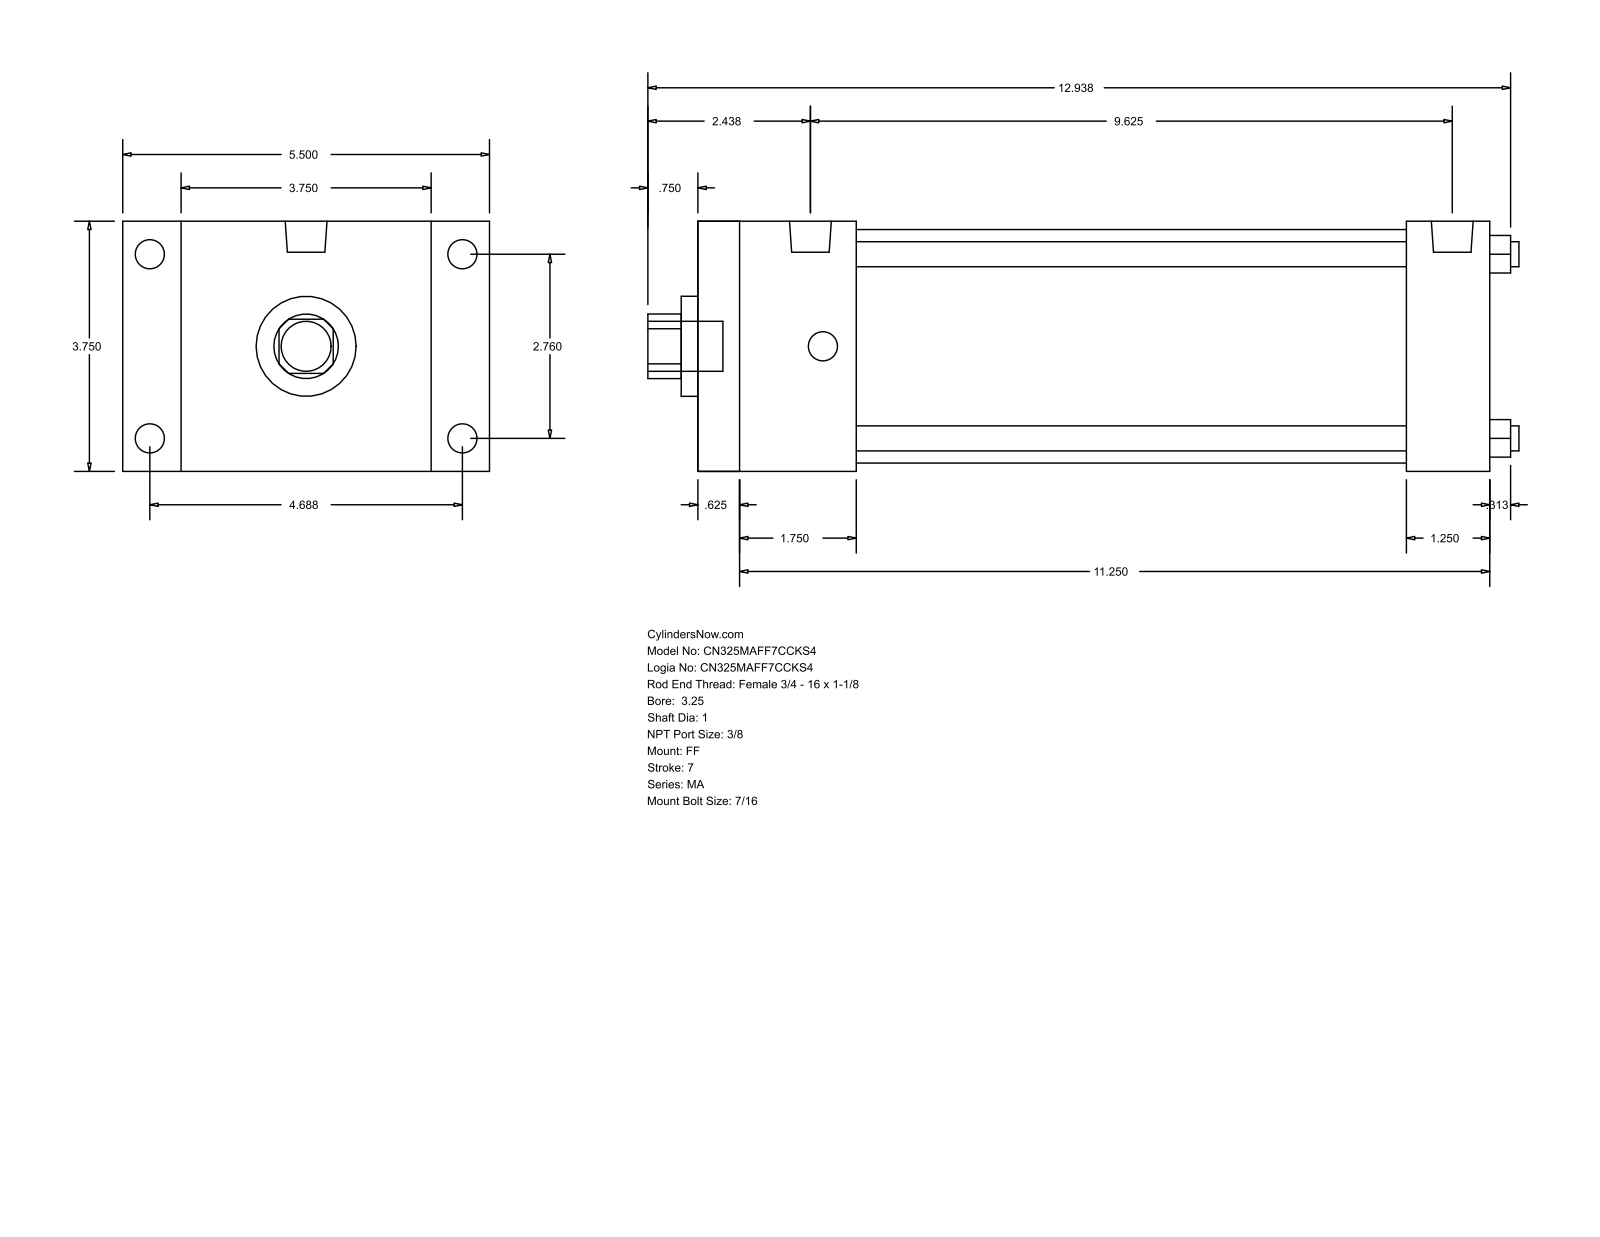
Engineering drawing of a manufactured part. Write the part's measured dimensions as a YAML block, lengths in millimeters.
part_name: "MA_FF__0325_1"
step_written_by: "GSSL Pune (CONFIG_CONTROL_DESIGN)"
units: millimeters
bodies: {solids: 0, faces: 92, planar: 64, cylindrical: 28, other: 0}
overall_size: [331.79, 139.7, 95.25]
round_holes:
  - {diameter: 9.53, count: 4}
  - {diameter: 25.4, count: 1}
  - {diameter: 38.1, count: 1}
  - {diameter: 88.9, count: 1}
round_bosses_or_shafts:
  - {diameter: 11.11, count: 8}
  - {diameter: 15.93, count: 2}
  - {diameter: 19.05, count: 1}
partial_cylinders:
  - {radius: 12.29, count: 1}
face_to_face_distances: [95.24, 301.63, 15.87, 285.76, 22.23, 117.47, 60.33, 269.88, 44.46, 254.01]
hole_center_spacings: [49.57, 70.1, 99.14]
